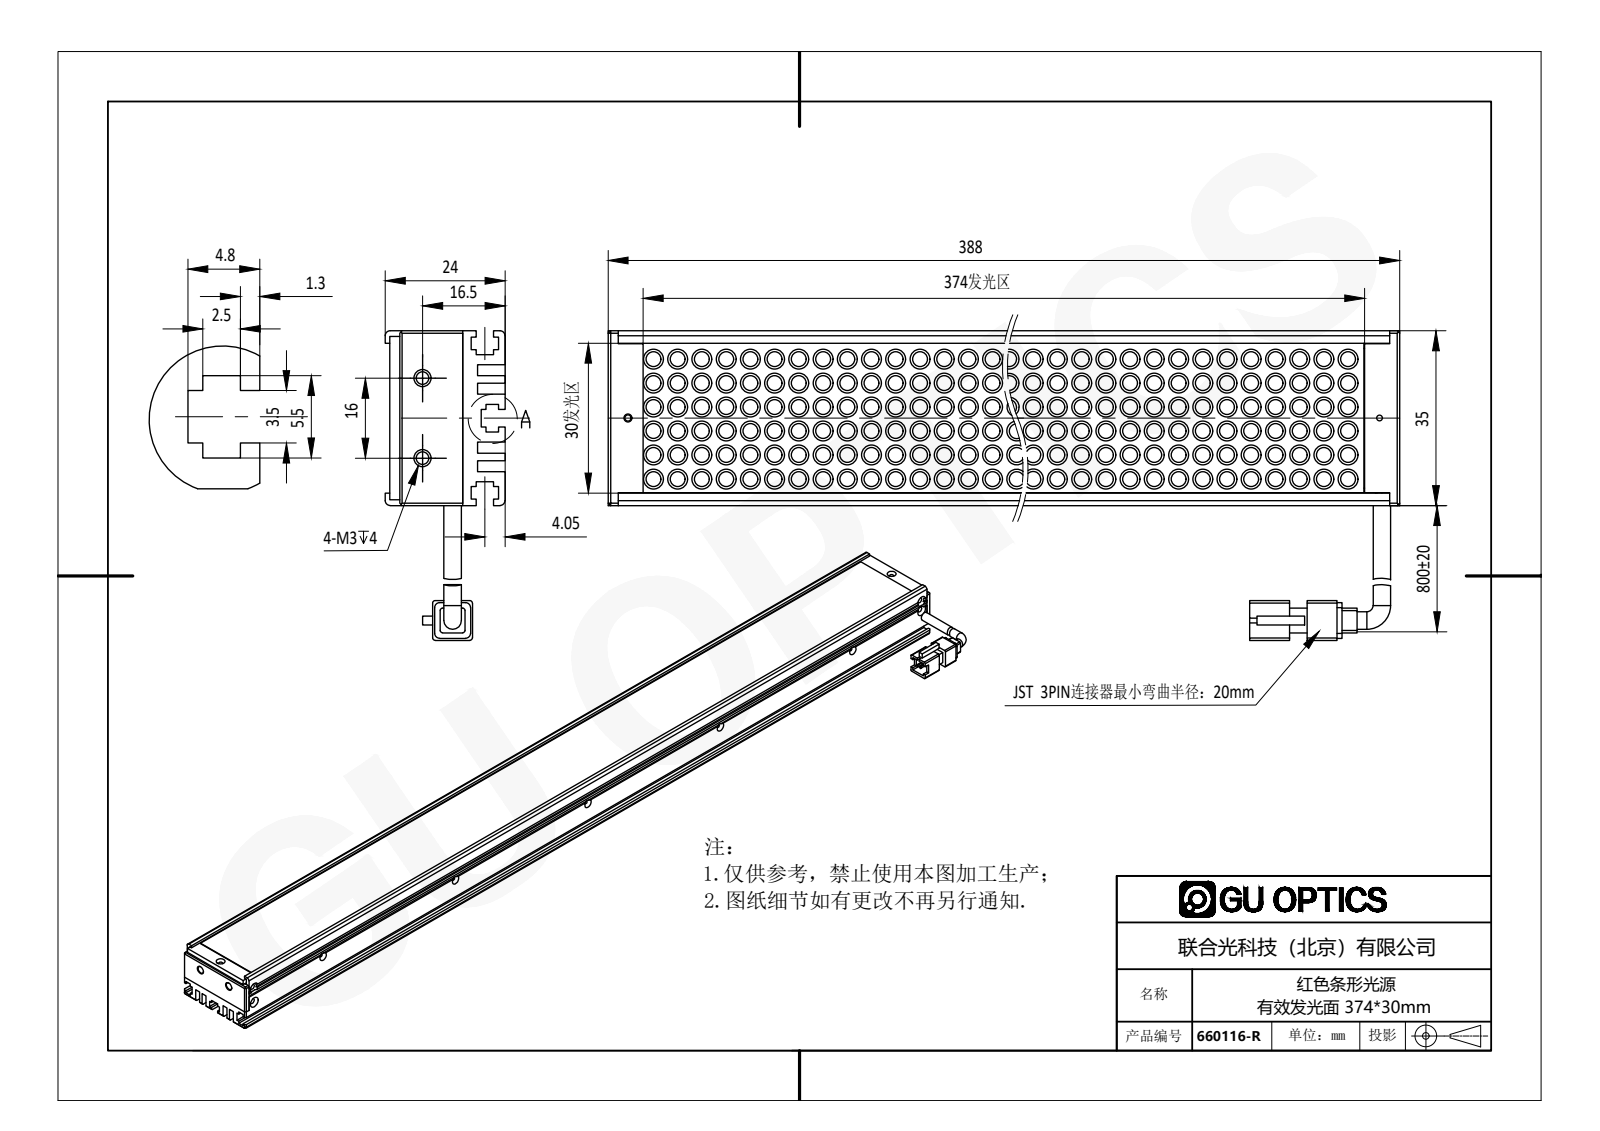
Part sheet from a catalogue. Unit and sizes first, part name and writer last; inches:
Units: inches
Overall size (bounding box): 15.276 × 2.441 × 0.945
Round holes (diameter × count): ⌀0.049 ×7, ⌀0.063 ×5, ⌀0.087 ×5, ⌀0.067 ×2, ⌀0.098 ×2, ⌀0.118 ×2
Round bosses / shafts (diameter × count): ⌀0.157 ×420, ⌀0.118 ×420, ⌀0.138 ×2
Partial cylindrical surfaces — rounded edges, fillets, slot ends (radius × count): R0.039 ×12, R0.02 ×8, R0.065 ×1
Main face-to-face distances: 0.079, 0.087, 0.472, 0.126, 0.039, 0.335, 0.346, 0.551, 0.433, 0.098
Hole centre spacings: 2.953, 14.961, 5.906, 0.022, 0.276, 7.442, 8.858, 13.347
Volume: 10.13 in³ · Surface area: 297.7 in²
Bodies: 9 solids, 3090 faces (746 planar, 1783 cylindrical, 561 other)
Part name (STEP PRODUCT): 660116-R
STEP written by: SolidWorks 2016 (AUTOMOTIVE_DESIGN)
